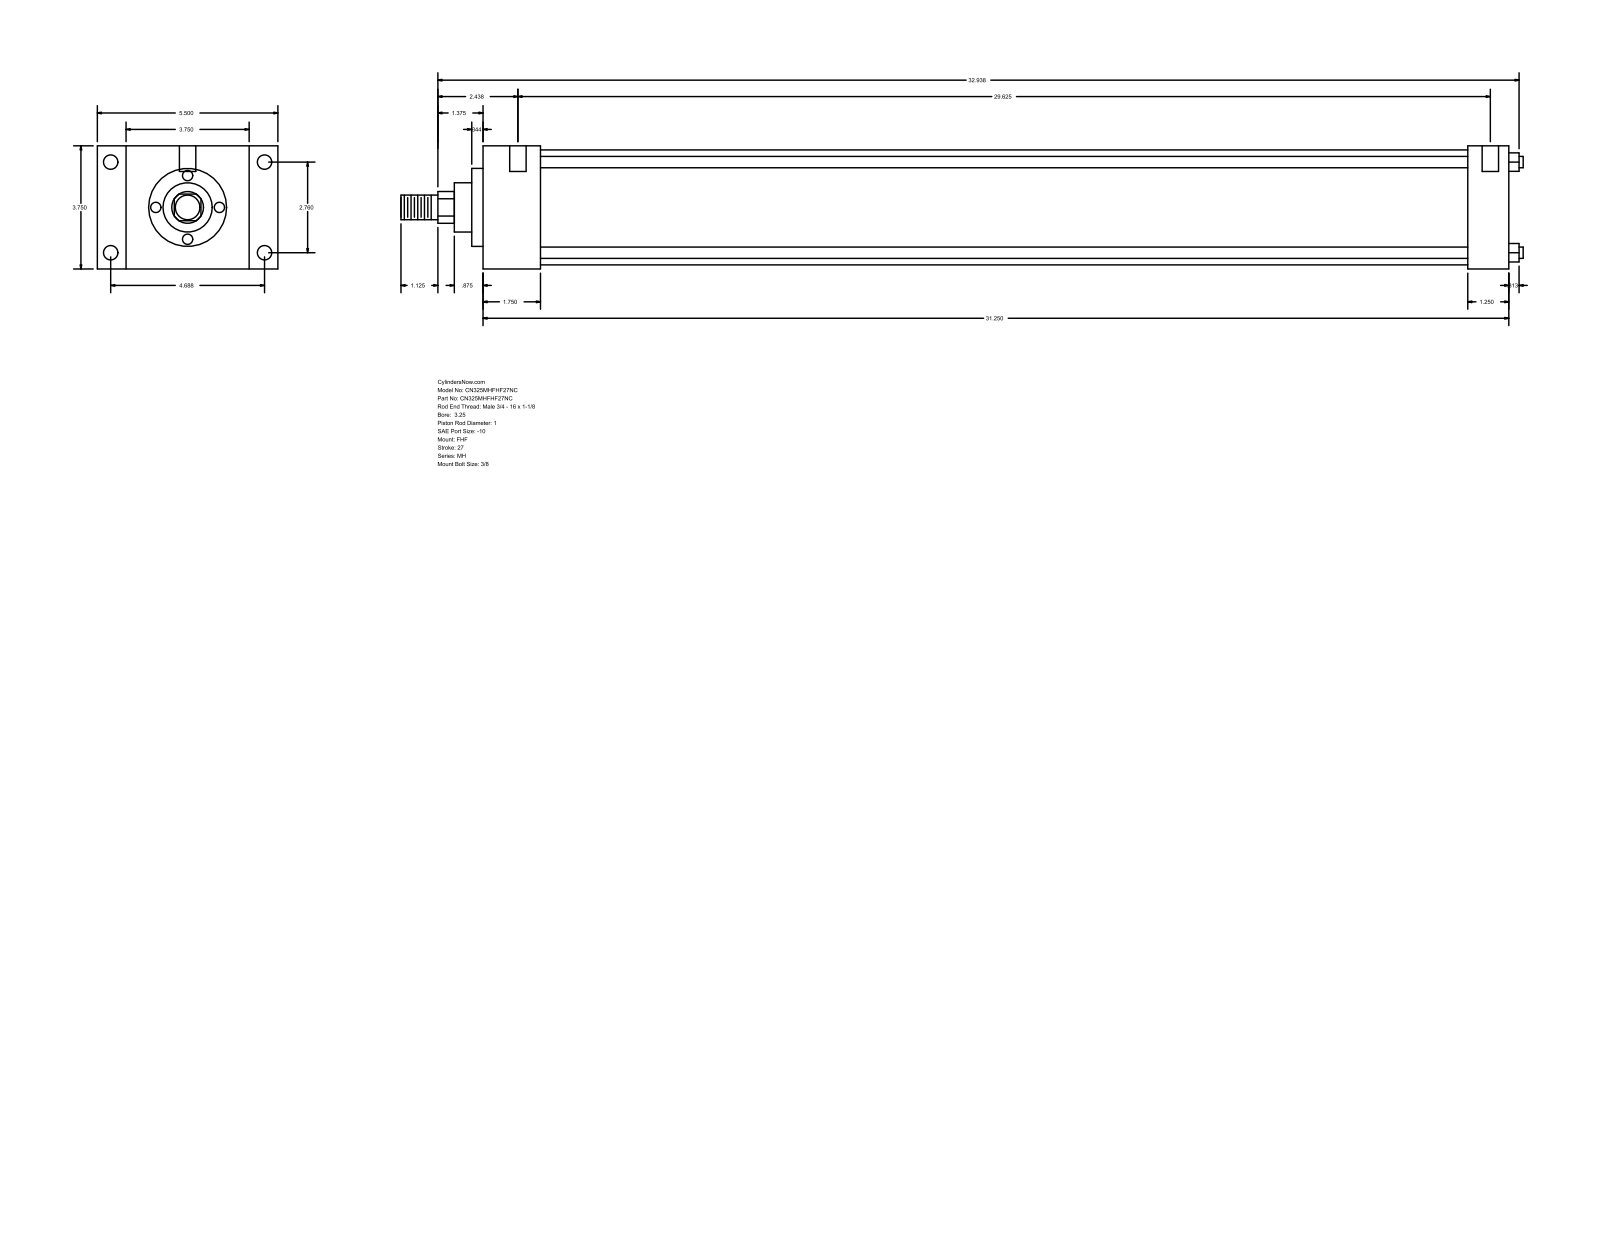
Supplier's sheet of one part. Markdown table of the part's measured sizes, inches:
| quantity | value |
| --- | --- |
| part name | MH_FHF__0325_1 |
| STEP written by | GSSL Pune (CONFIG_CONTROL_DESIGN) |
| units | inches |
| bodies | 0 solids, 90 faces (61 planar, 29 cylindrical, 0 other) |
| overall size | 34.187 × 5.5 × 3.75 |
| round holes (diameter × count) | 0.219 × 4, 0.438 × 4, 0.5 × 2 |
| round bosses / shafts (diameter × count) | 0.345 × 4, 3.5 × 1, 2.375 × 1, 1.5 × 1, 1 × 1, 0.75 × 1 |
| partial cylindrical surfaces (radius × count) | 0.484 × 1 |
| main face-to-face distances | 3.75, 31.25, 1.75, 29.5, 0.875, 4.625, 5.5, 30, 28.25, 1.25 |
| hole center spacings | 2.76, 4.687, 5.439, 29.875, 0.062, 0.187, 29.625, 29.687 |
